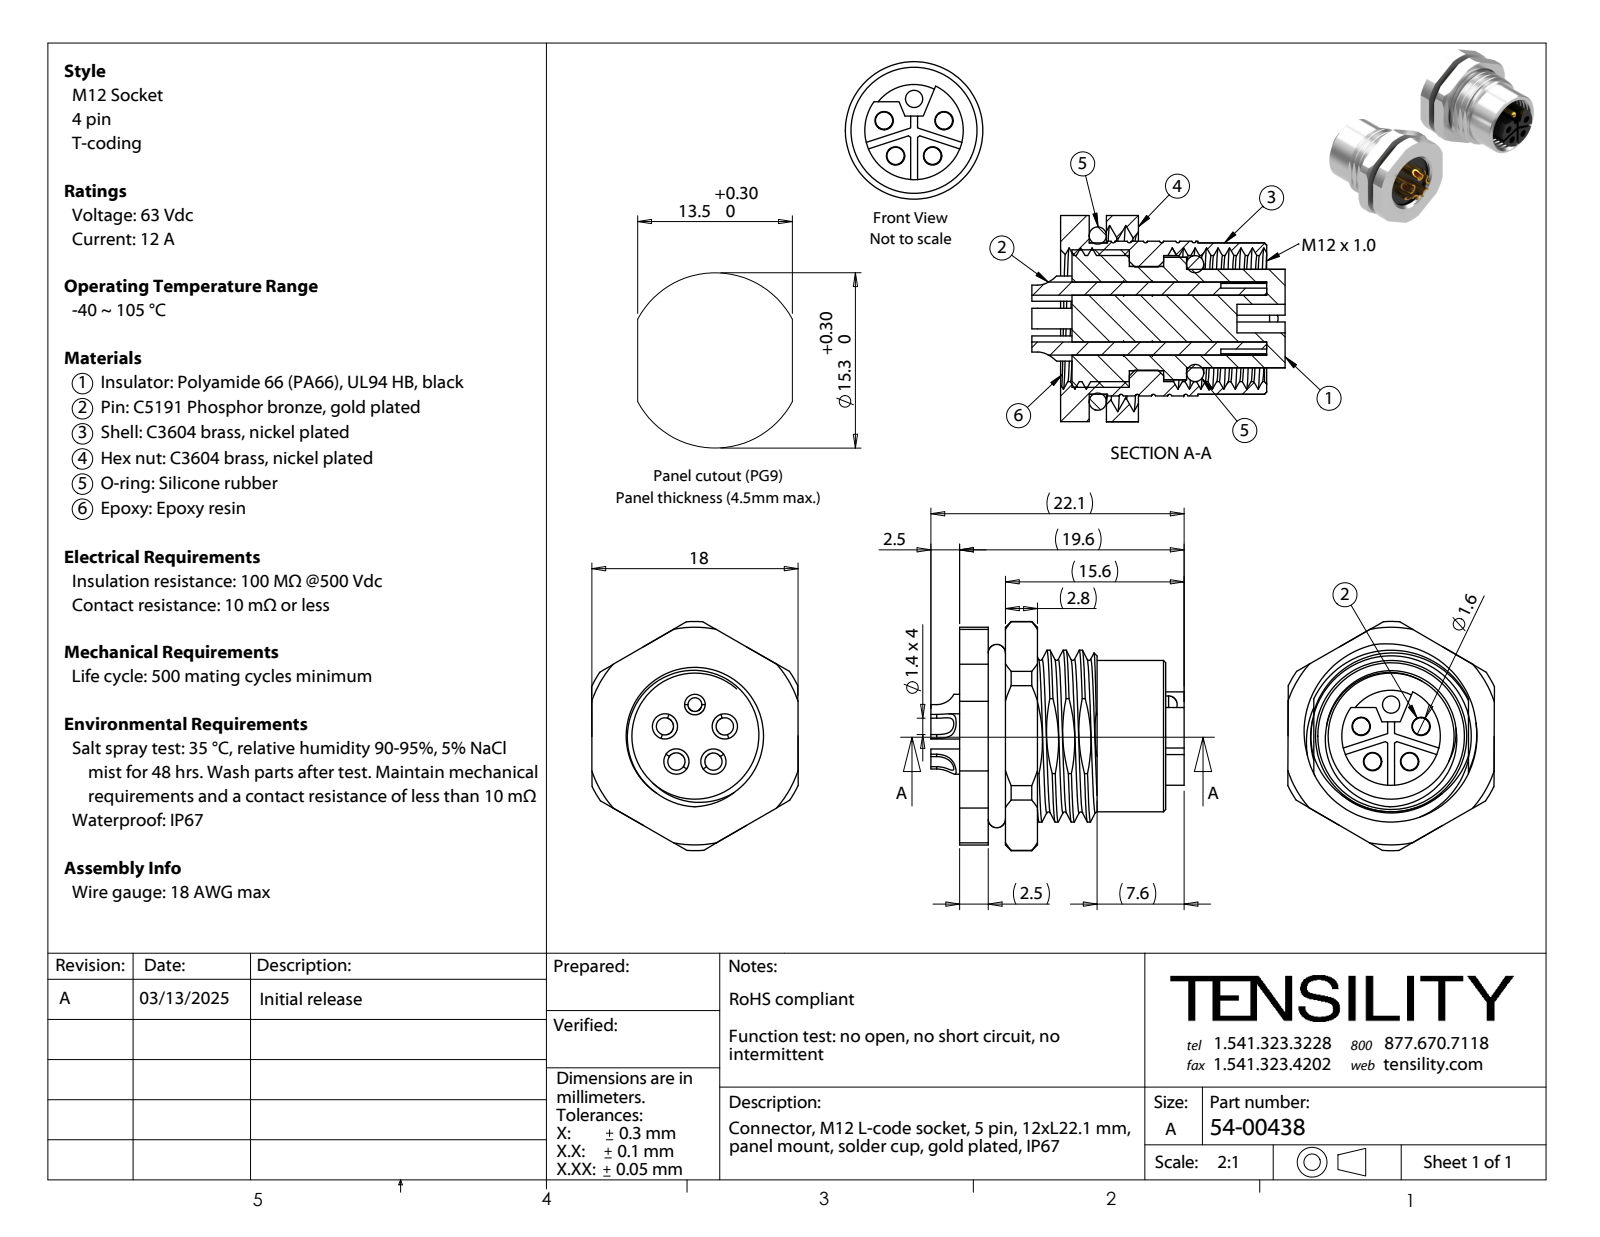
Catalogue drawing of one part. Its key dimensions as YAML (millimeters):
part_name: "54-00438; 54-00438-04; 54-00438-03; 54-00438-06 (+4 more)"
step_written_by: "SolidWorks 2021 (CONFIG_CONTROL_DESIGN)"
units: millimeters
bodies: {solids: 10, faces: 363, planar: 124, cylindrical: 142, other: 97}
overall_size: [22.1, 19.8, 19.44]
volume: 2917
surface_area: 5684
round_holes:
  - {diameter: 1.5, count: 5}
  - {diameter: 1.6, count: 4}
  - {diameter: 1.2, count: 1}
  - {diameter: 9, count: 1}
  - {diameter: 11, count: 1}
  - {diameter: 14, count: 1}
round_bosses_or_shafts:
  - {diameter: 2.2, count: 4}
  - {diameter: 13.2, count: 1}
  - {diameter: 12, count: 1}
  - {diameter: 10.7, count: 1}
  - {diameter: 9.1, count: 1}
  - {diameter: 8.6, count: 1}
  - {diameter: 1.8, count: 1}
partial_cylinders:
  - {radius: 1.86, count: 4}
  - {radius: 1.7, count: 1}
  - {radius: 7.5, count: 1}
  - {radius: 9.5, count: 1}
  - {radius: 10, count: 1}
face_to_face_distances: [1.5, 2.5, 18, 5, 3, 1, 2, 4, 6, 6.8]
hole_center_spacings: [2.75, 5.23, 3.24, 3.23, 5.24]
